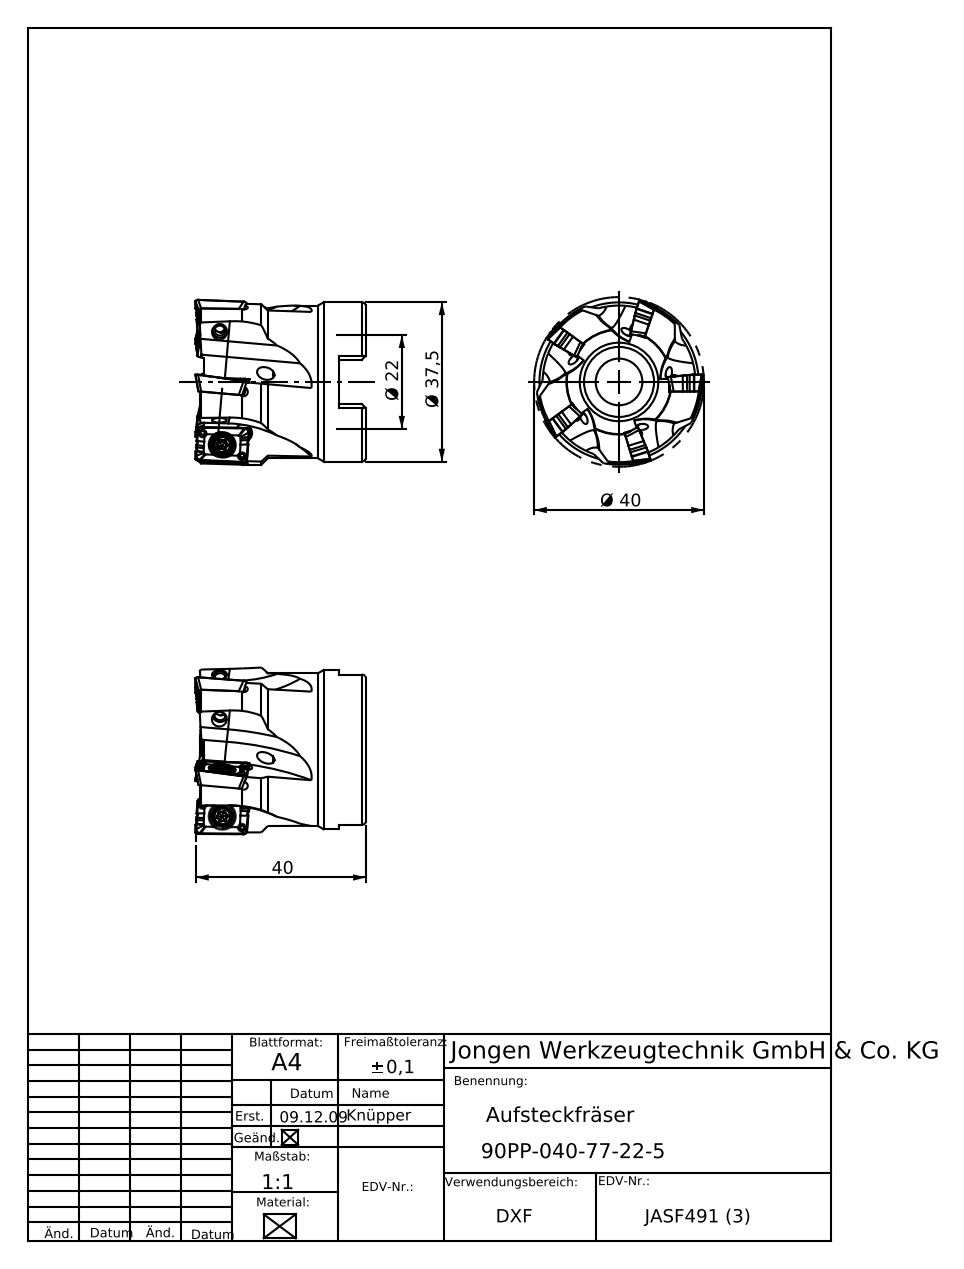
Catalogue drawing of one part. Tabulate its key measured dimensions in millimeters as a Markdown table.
| quantity | value |
| --- | --- |
| part name | 90PP-040-77-22-5 |
| STEP written by | SolidWorks 2012 (AUTOMOTIVE_DESIGN) |
| units | millimeters |
| bodies | 1 solid, 137 faces (46 planar, 48 cylindrical, 43 other) |
| overall size | 40.03 × 40.03 × 40 |
| volume | 30 367 mm³ |
| surface area | 10 283 mm² |
| round holes (diameter × count) | 3 × 5, 11 × 1, 16.5 × 1, 22 × 1, 22.15 × 1, 22.3 × 1 |
| round bosses / shafts (diameter × count) | 38 × 1, 36 × 1 |
| partial cylindrical surfaces (radius × count) | 2 × 5, 10 × 5, 26.35 × 5, 19.5 × 1 |
| main face-to-face distances | 21.95, 6.3, 15.65, 38.1, 31.8, 16.15, 27.1, 20.8, 5.15, 11 |
